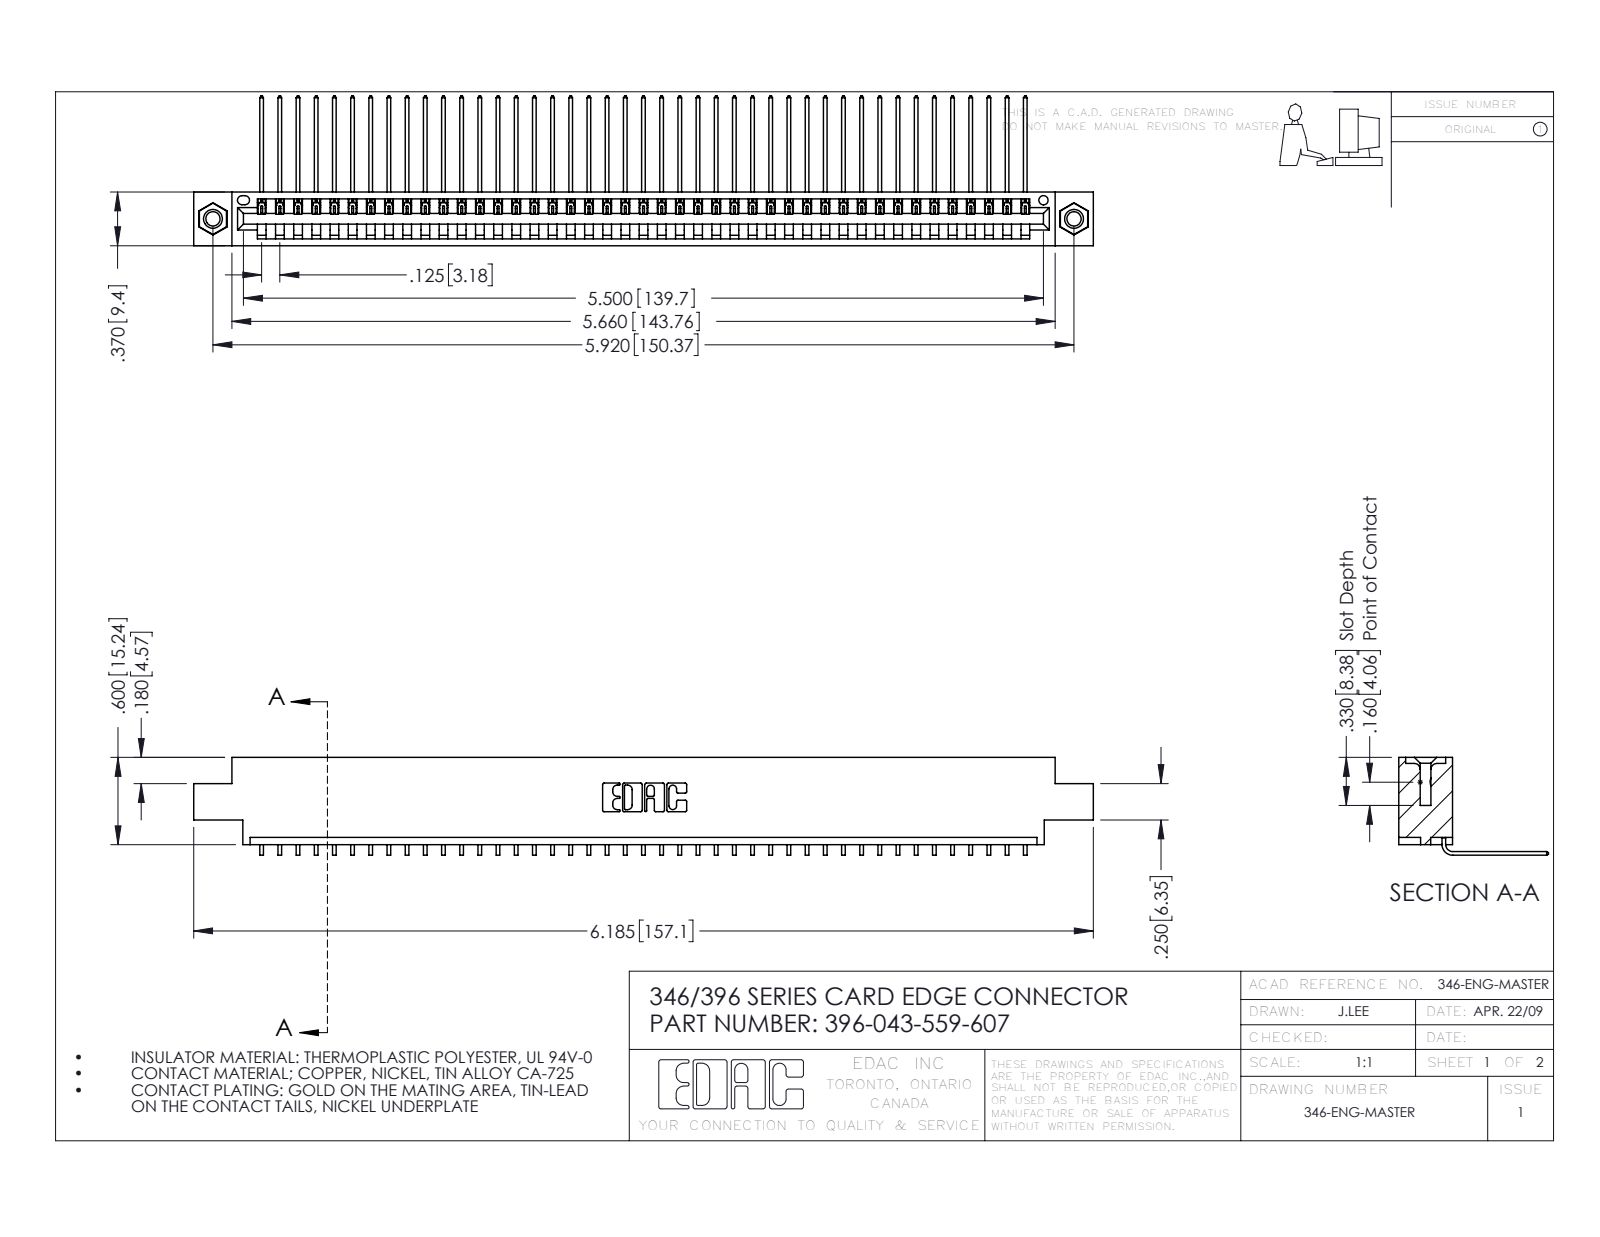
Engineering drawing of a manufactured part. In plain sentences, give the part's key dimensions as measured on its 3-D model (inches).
The part is named "345-292-001_558 559 Tail - 1; 346 Part_0.170 Offset - 0.156 Dia-TI; 396-043-559-607; 345-250-001_345-250-005-103". Its 3-D file was written by "SolidWorks 2016 (CONFIG_CONTROL_DESIGN)". It is 46 solids with 2766 faces: 1918 planar, 832 cylindrical and 16 other. Overall it measures 6.185 by 1.03 by 0.673 inches. Its volume is 0.917 cubic inches and its surface area 30.74 square inches. Round holes: 2 of diameter 0.098, 2 of diameter 0.125, 2 of diameter 0.156, 1 of diameter 0.064. Round bosses or shafts: 2 of diameter 0.155. Partial cylindrical surfaces (rounded edges, fillets, slot ends): 86 of radius 0.006, 22 of radius 0.01, 6 of radius 0.007, 6 of radius 0.031, 3 of radius 0.026, 2 of radius 0.031, 2 of radius 0.04, 1 of radius 0.014. The main face-to-face distances are 0.048, 0.322, 0.37, 0.025, 0.25, 0.072, 0.222, 0.148, 0.298, 0.1. The hole center spacings are 0.246, 5.711, 5.92.
